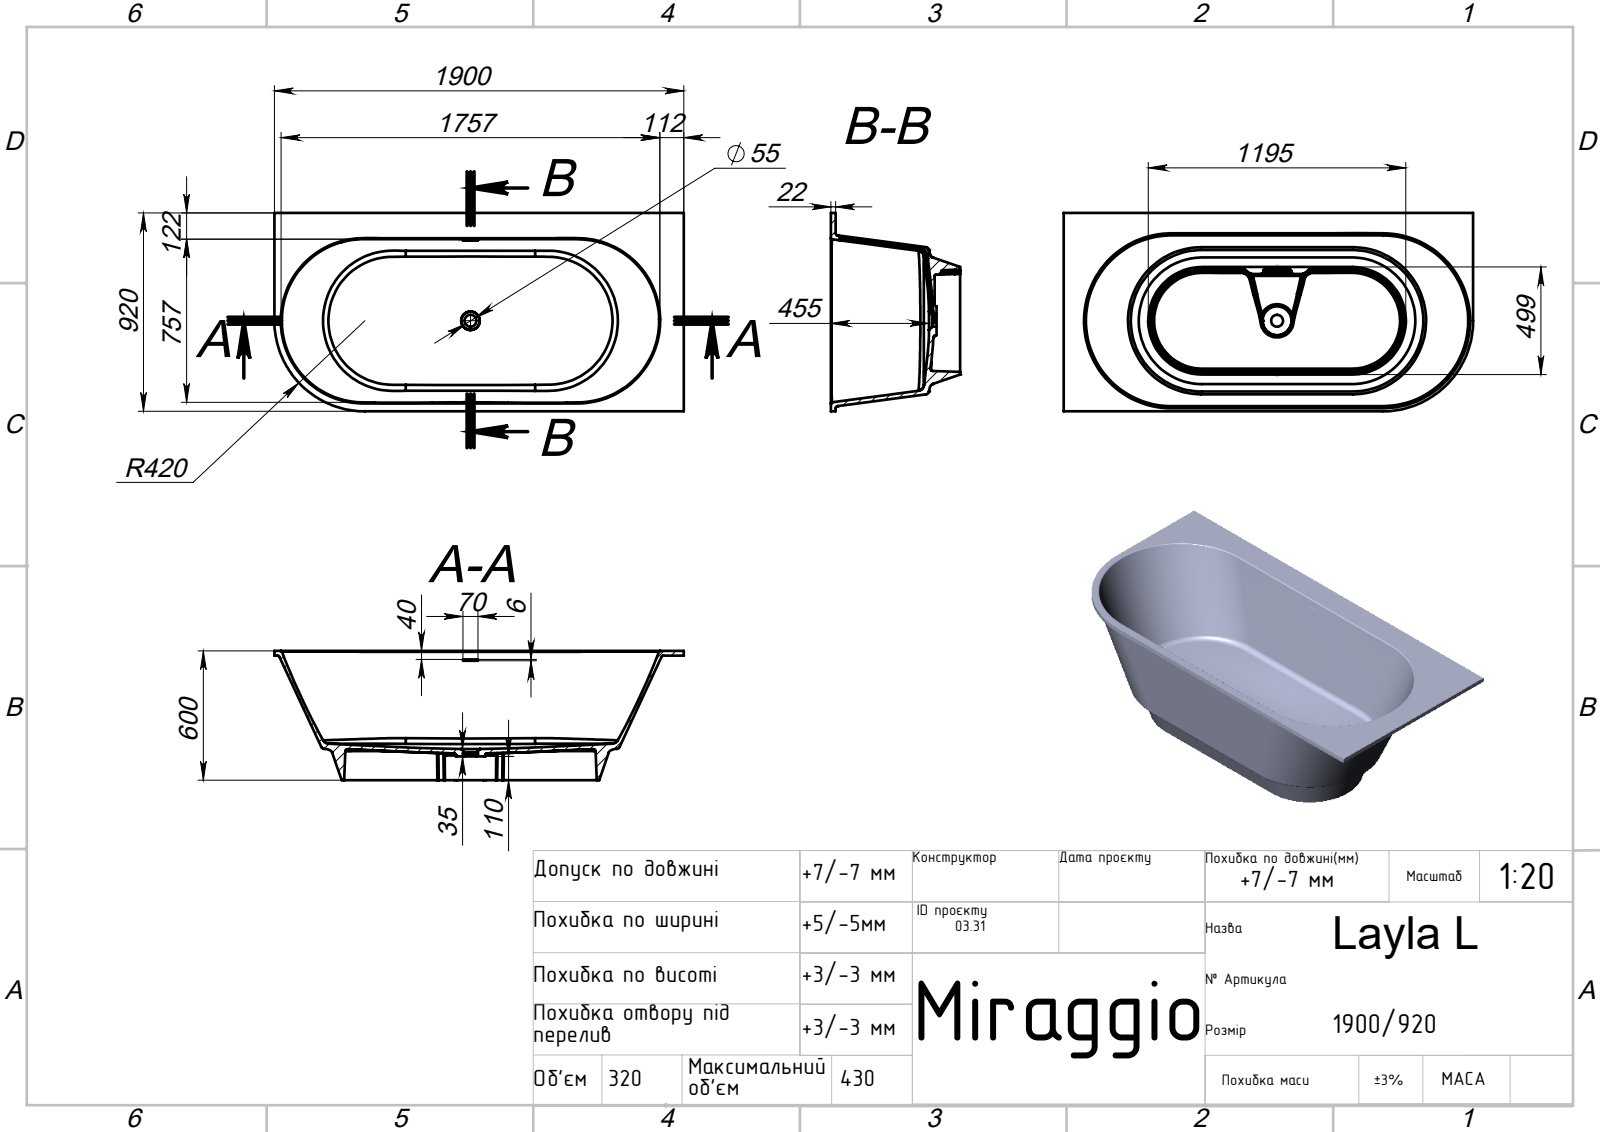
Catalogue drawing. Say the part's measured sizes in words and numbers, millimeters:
The part is named "Layla L". Its 3-D file was written by "SolidWorks 2020 (AUTOMOTIVE_DESIGN)". It is 1 solid with 111 faces: 28 planar, 18 cylindrical and 65 other. Overall it measures 1900 by 920 by 600 millimeters. Its volume is 83 280 000 cubic millimeters and its surface area 6 978 000 square millimeters. Round holes: 1 of diameter 55. Partial cylindrical surfaces (rounded edges, fillets, slot ends): 4 of radius 10, 3 of radius 5, 2 of radius 3, 1 of radius 37, 1 of radius 46, 1 of radius 62.5, 1 of radius 198.58, 1 of radius 237.27. The main face-to-face distances are 22, 578, 600, 920, 119, 459, 481, 110, 9, 468.
